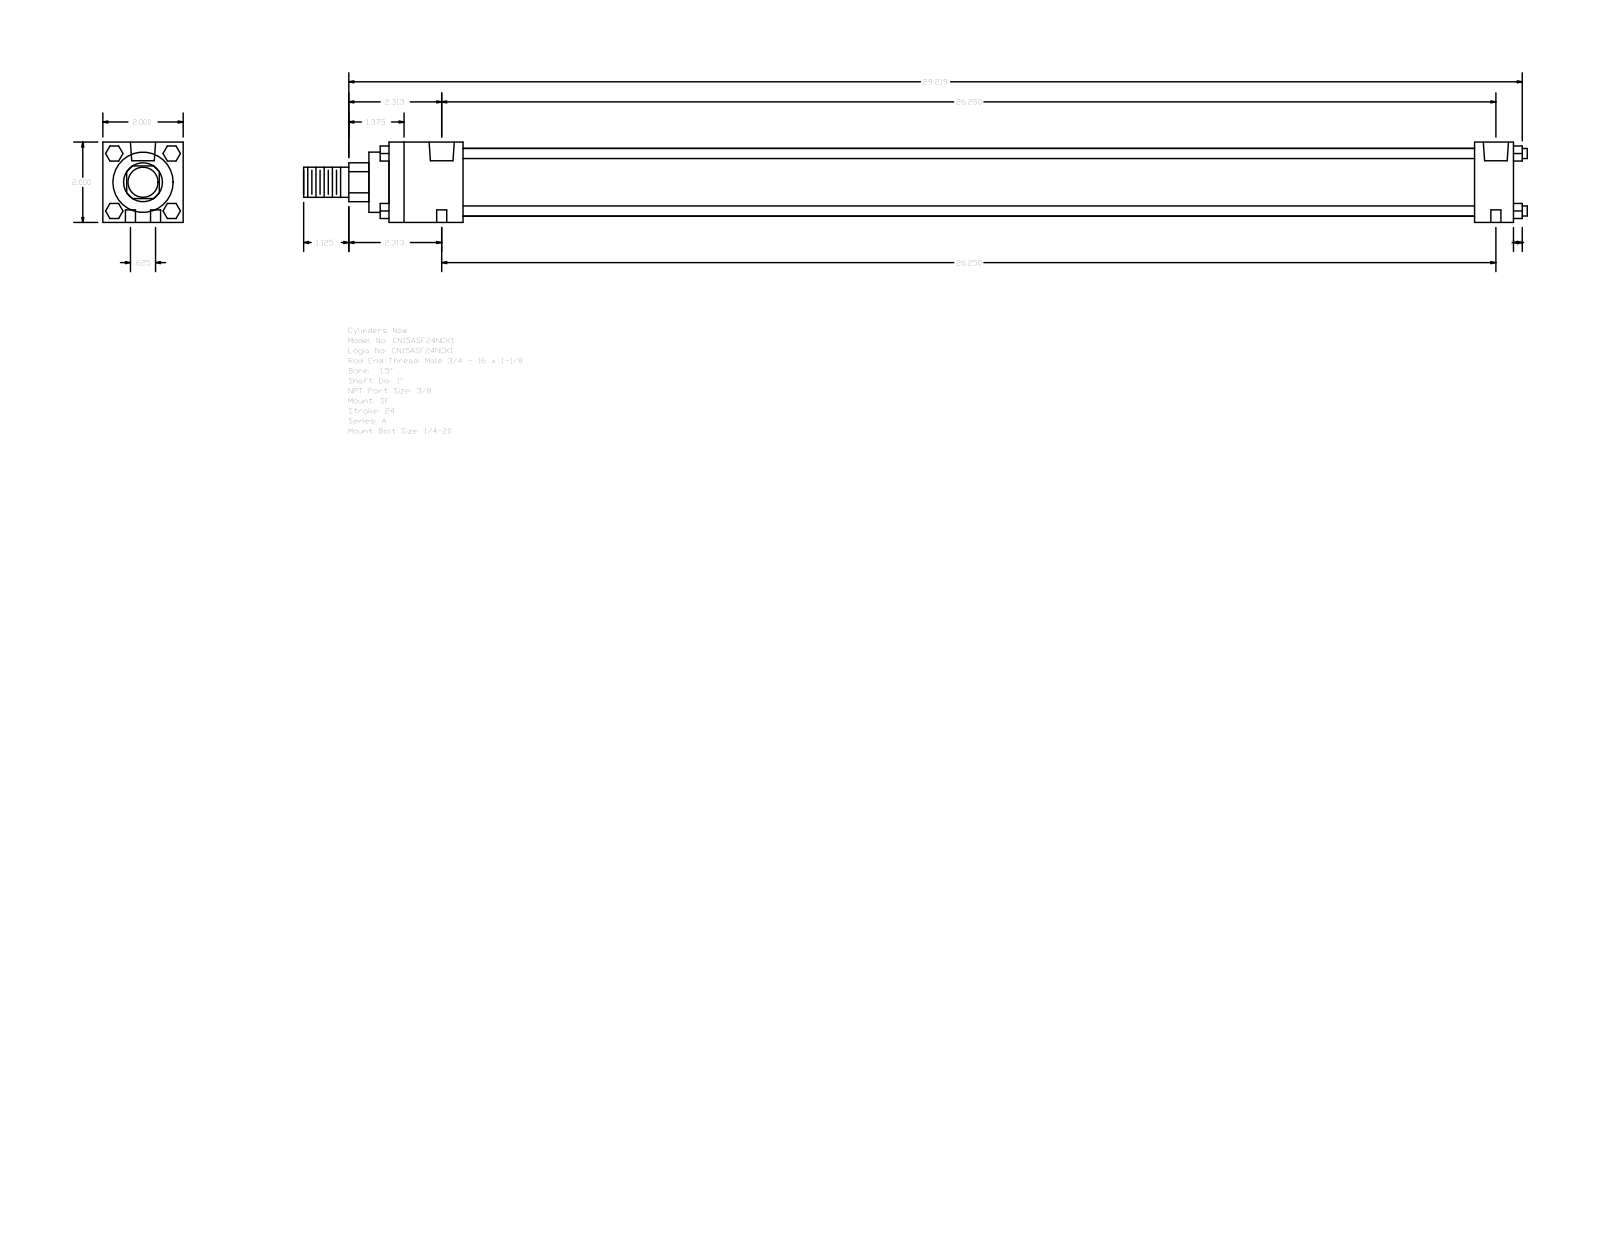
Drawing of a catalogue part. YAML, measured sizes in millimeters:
part_name: "A_SF__0150_1"
step_written_by: "GSSL Pune (CONFIG_CONTROL_DESIGN)"
units: millimeters
bodies: {solids: 0, faces: 124, planar: 94, cylindrical: 30, other: 0}
overall_size: [773.91, 50.8, 50.8]
round_holes:
  - {diameter: 6.35, count: 4}
  - {diameter: 5.56, count: 2}
  - {diameter: 15.93, count: 2}
round_bosses_or_shafts:
  - {diameter: 6.35, count: 4}
  - {diameter: 42.93, count: 1}
  - {diameter: 38.1, count: 1}
  - {diameter: 25.4, count: 1}
  - {diameter: 19.05, count: 1}
partial_cylinders:
  - {radius: 12.29, count: 1}
face_to_face_distances: [50.8, 711.2, 46.83, 686.59, 639.76, 664.37, 24.61, 12.7, 59.53, 699.29]
hole_center_spacings: [7.94, 666.8, 666.75, 15.88, 666.94, 658.81]
